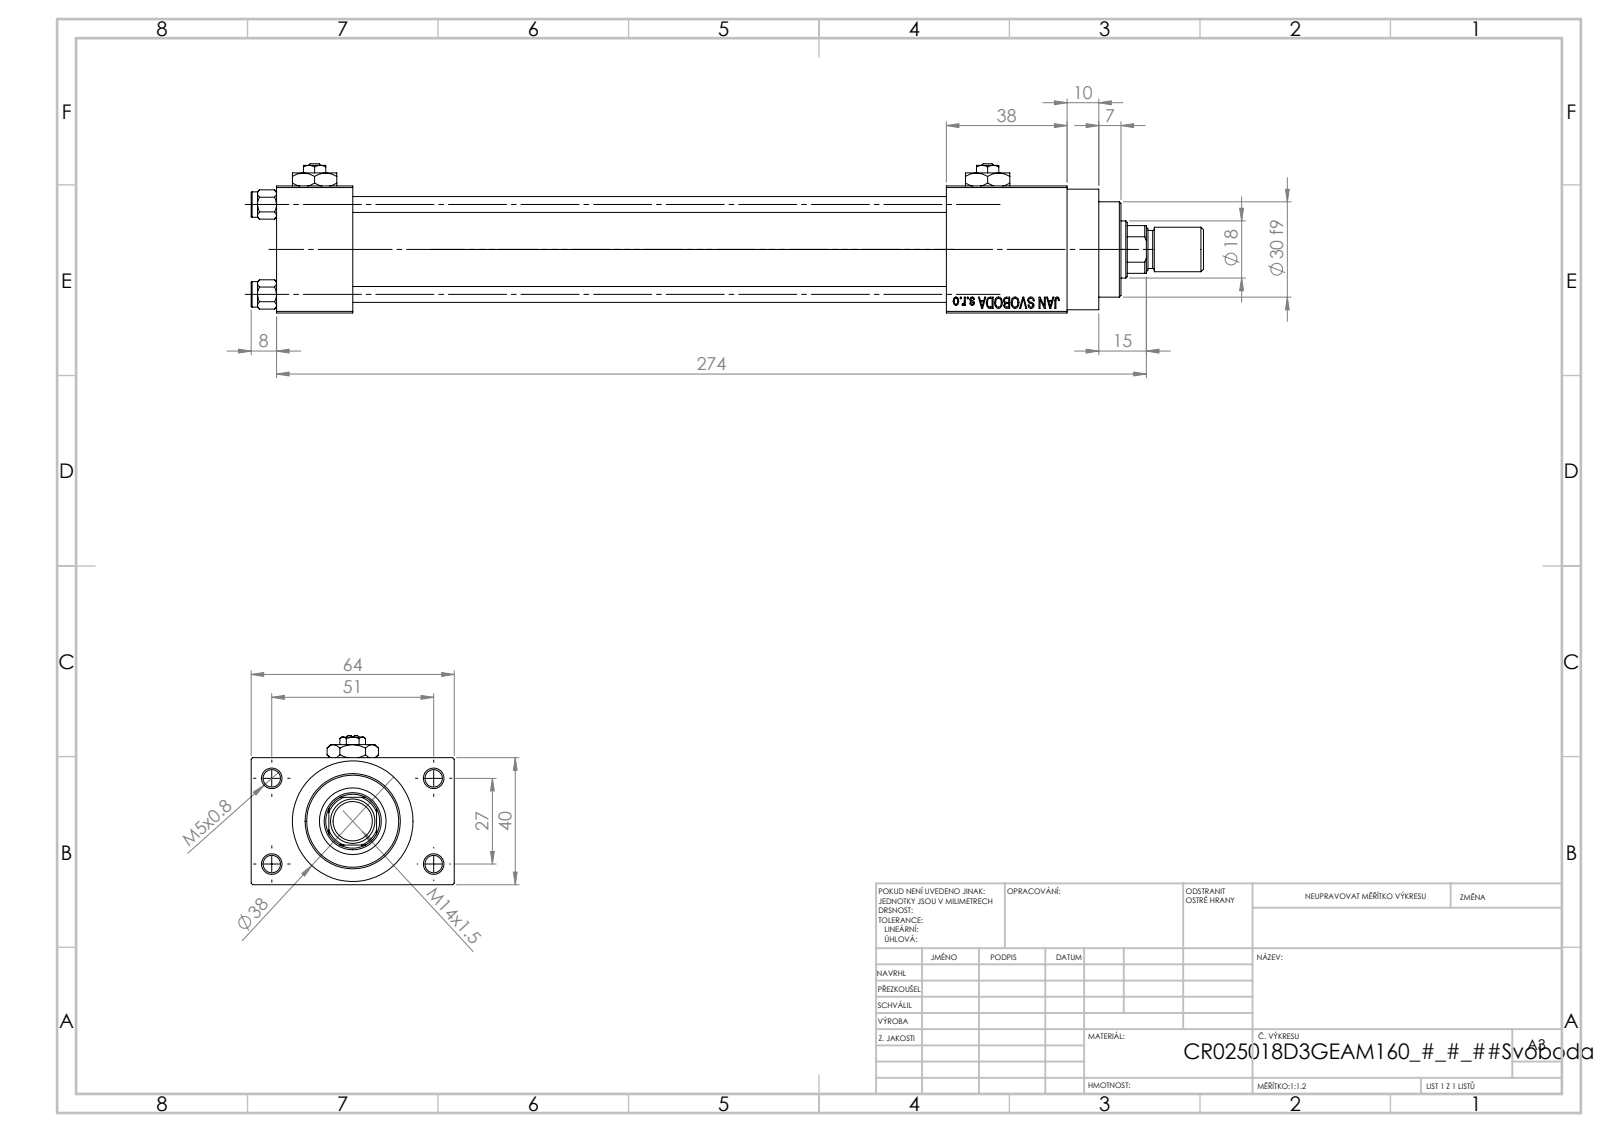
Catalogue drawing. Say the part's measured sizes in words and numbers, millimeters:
The part is named "NUT_M5_D; V215_VC_A; V215CR_D_TYCINKA; ROD_END_AH (+3 more)". Its 3-D file was written by "SolidWorks 2019 (CONFIG_CONTROL_DESIGN)". It is 14 solids with 1213 faces: 545 planar, 102 cylindrical and 566 other. Overall it measures 300 by 64 by 47 millimeters. Its volume is 266 001 cubic millimeters and its surface area 108 334 square millimeters. Round holes: 4 of diameter 5, 4 of diameter 5.5, 3 of diameter 20, 2 of diameter 7, 2 of diameter 13.16, 1 of diameter 8.5, 1 of diameter 18, 1 of diameter 21, 1 of diameter 25, 1 of diameter 30. Round bosses or shafts: 4 of diameter 8, 1 of diameter 38, 1 of diameter 31, 1 of diameter 14, 1 of diameter 12. Partial cylindrical surfaces (rounded edges, fillets, slot ends): 1 of radius 8.5. The main face-to-face distances are 40, 12, 52, 187, 24, 211, 64, 38, 225, 249. The hole center spacings are 11.37, 20.01, 28.3, 28.85, 29.89, 39.66, 48.34, 27.
